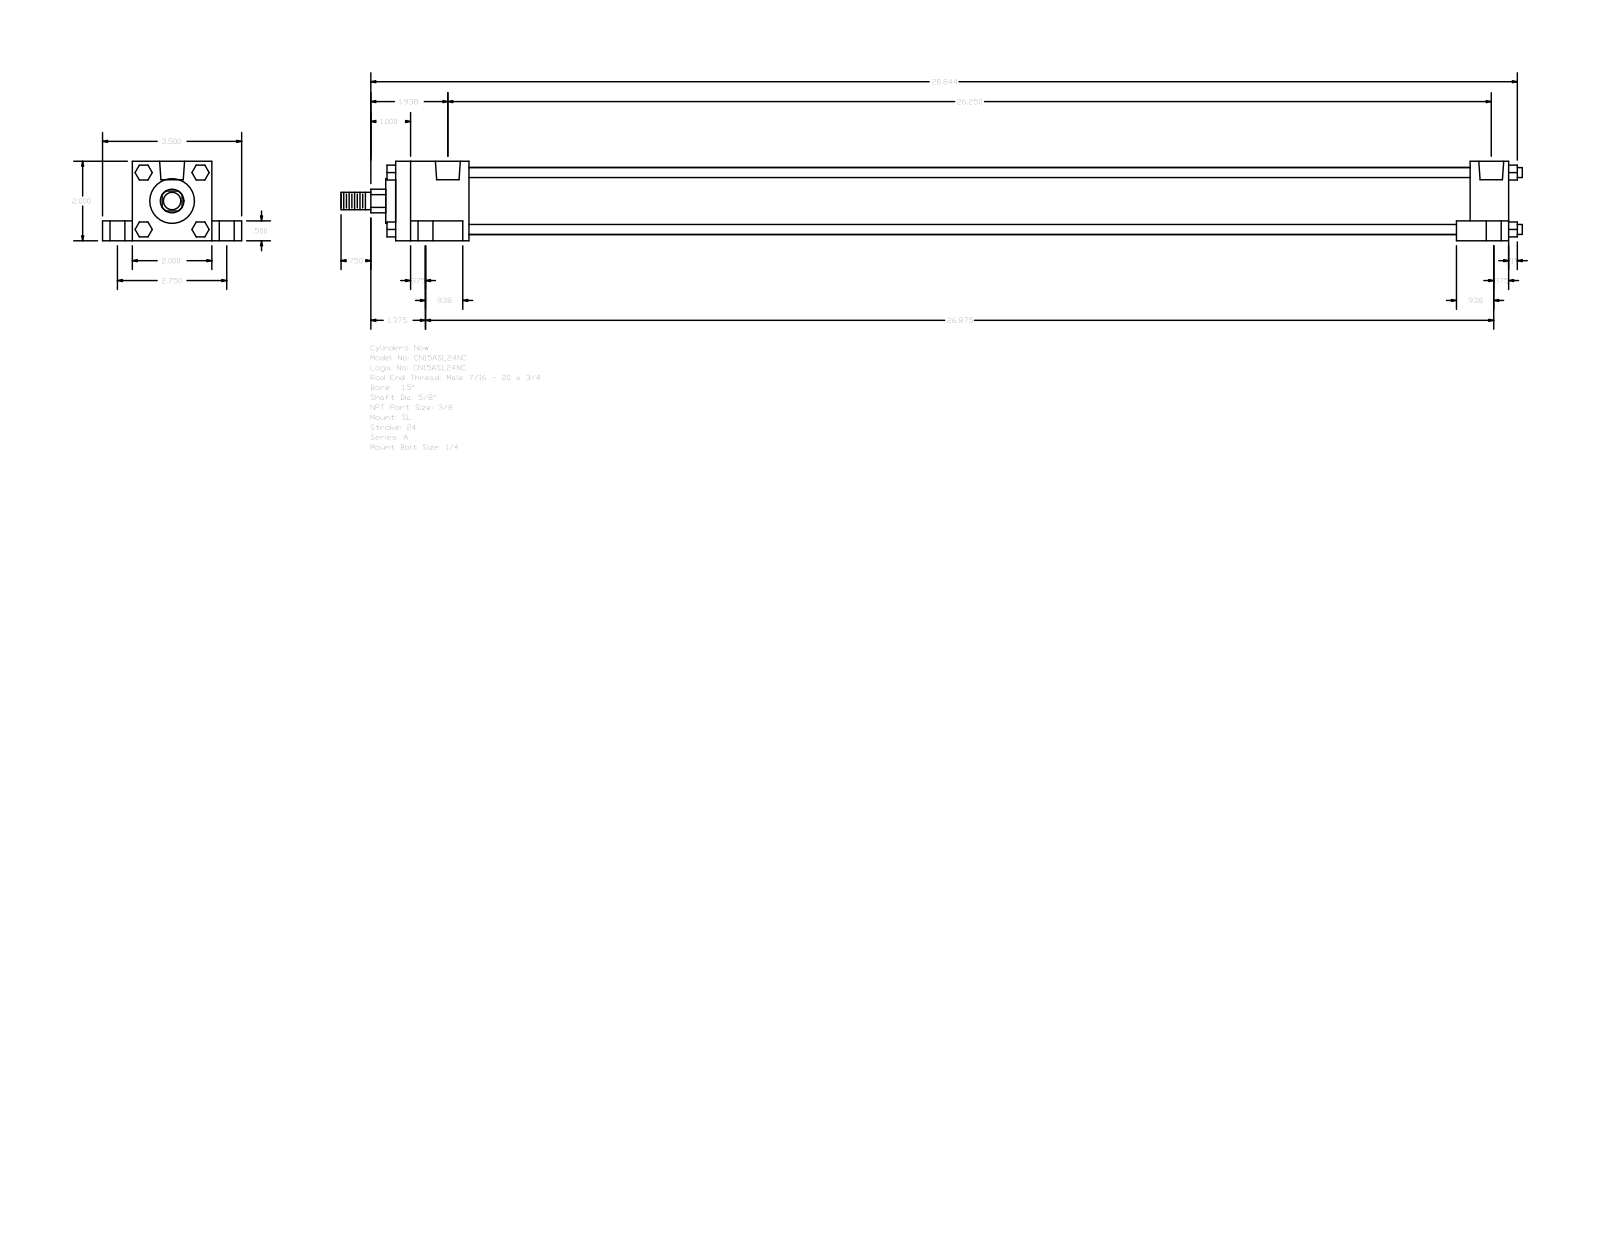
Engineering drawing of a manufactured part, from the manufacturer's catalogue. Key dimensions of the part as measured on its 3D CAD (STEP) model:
Part name (STEP PRODUCT): A_SL__0150_0.625
STEP written by: GSSL Pune (CONFIG_CONTROL_DESIGN)
Units: millimetres
Bodies: 0 solids, 148 faces (112 planar, 36 cylindrical, 0 other)
Overall size (bounding box): 754.86 × 88.9 × 50.8
Round holes (diameter × count): ⌀5.56 ×4, ⌀9.53 ×4, ⌀15.88 ×4, ⌀15.93 ×2
Round bosses / shafts (diameter × count): ⌀6.35 ×4, ⌀42.93 ×1, ⌀28.57 ×1, ⌀15.88 ×1, ⌀11.11 ×1
Partial cylindrical surfaces — rounded edges, fillets, slot ends (radius × count): R7.54 ×1
Main face-to-face distances: 50.8, 19.05, 38.1, 12.7, 69.85, 711.2, 9.52, 33.34, 686.59, 24.61
Hole centre spacings: 3.97, 34.96, 35.36, 37.73, 39.41, 69.84, 658.81, 662.78
